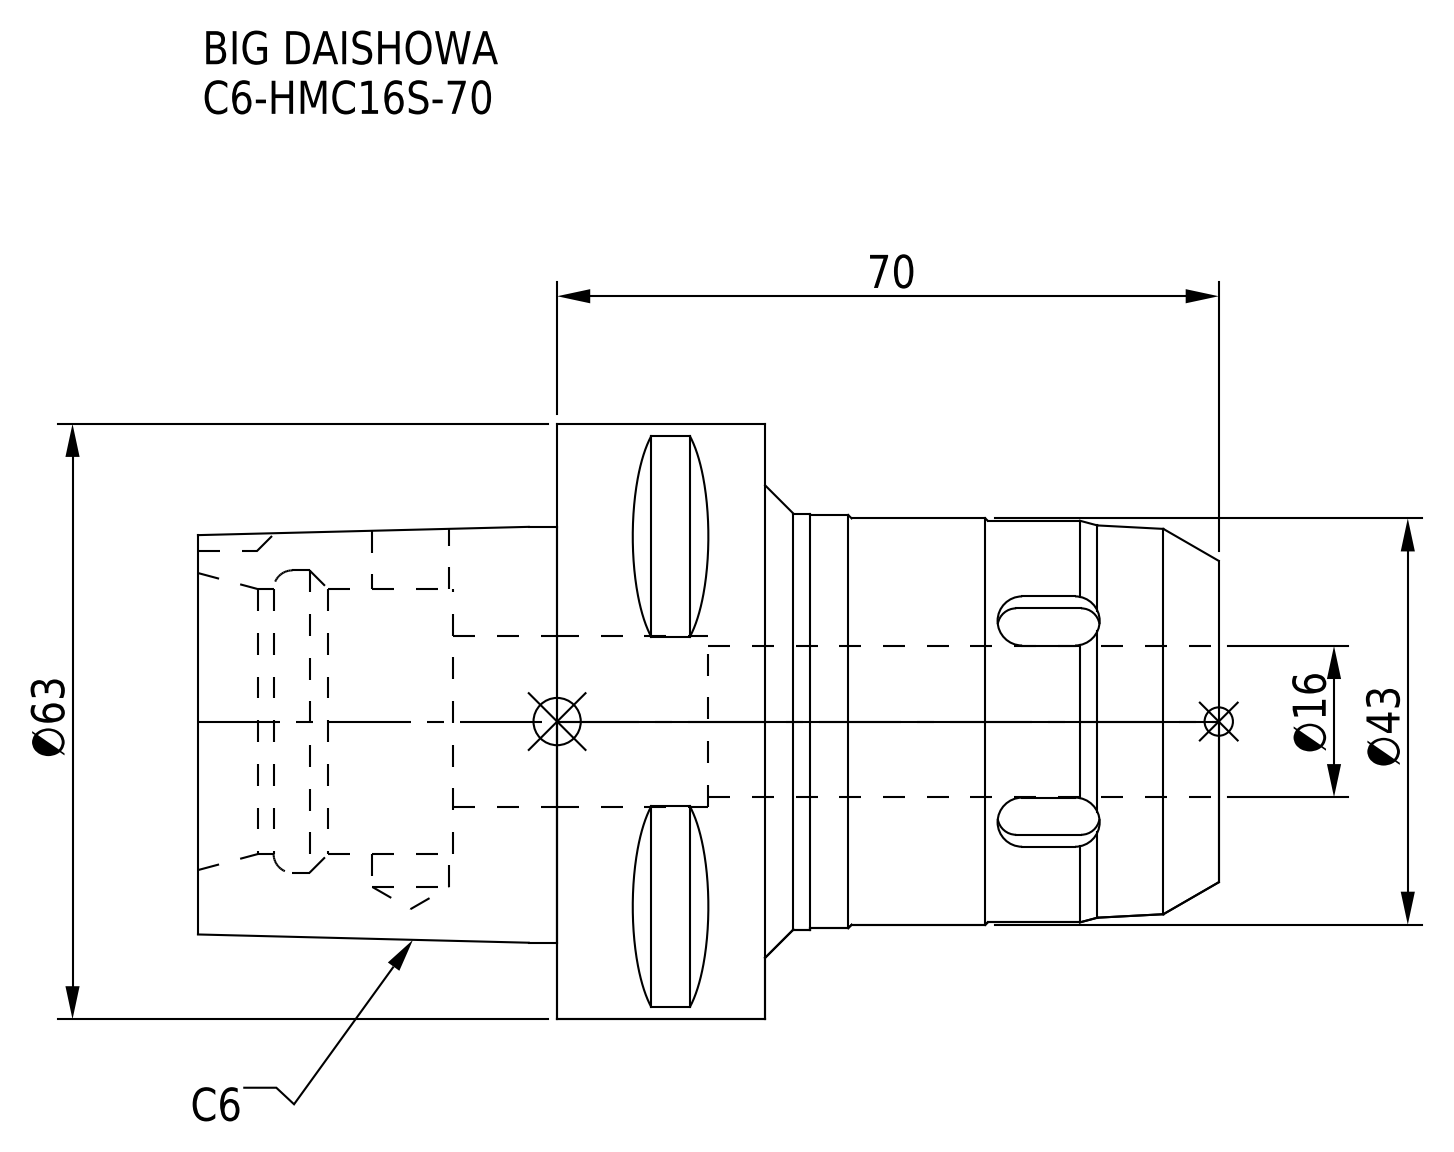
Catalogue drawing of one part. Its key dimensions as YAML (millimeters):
part_name: "C6-HMC16S-70"
step_written_by: "CREO PARAMETRIC BY PTC INC, 2016380 (AUTOMOTIVE_DESIGN)"
units: millimeters
bodies: {solids: 1, faces: 110, planar: 47, cylindrical: 37, other: 26}
overall_size: [108, 63, 63]
volume: 152499
surface_area: 28472
round_holes:
  - {diameter: 8.1, count: 1}
  - {diameter: 16, count: 1}
  - {diameter: 18, count: 1}
  - {diameter: 28, count: 1}
  - {diameter: 32, count: 1}
round_bosses_or_shafts:
  - {diameter: 63, count: 1}
  - {diameter: 44, count: 1}
  - {diameter: 43.7, count: 1}
  - {diameter: 43, count: 1}
  - {diameter: 42.5, count: 1}
partial_cylinders:
  - {radius: 3, count: 6}
  - {radius: 5, count: 1}
face_to_face_distances: [22, 48, 70, 38, 108, 60, 27, 81, 33, 11]
